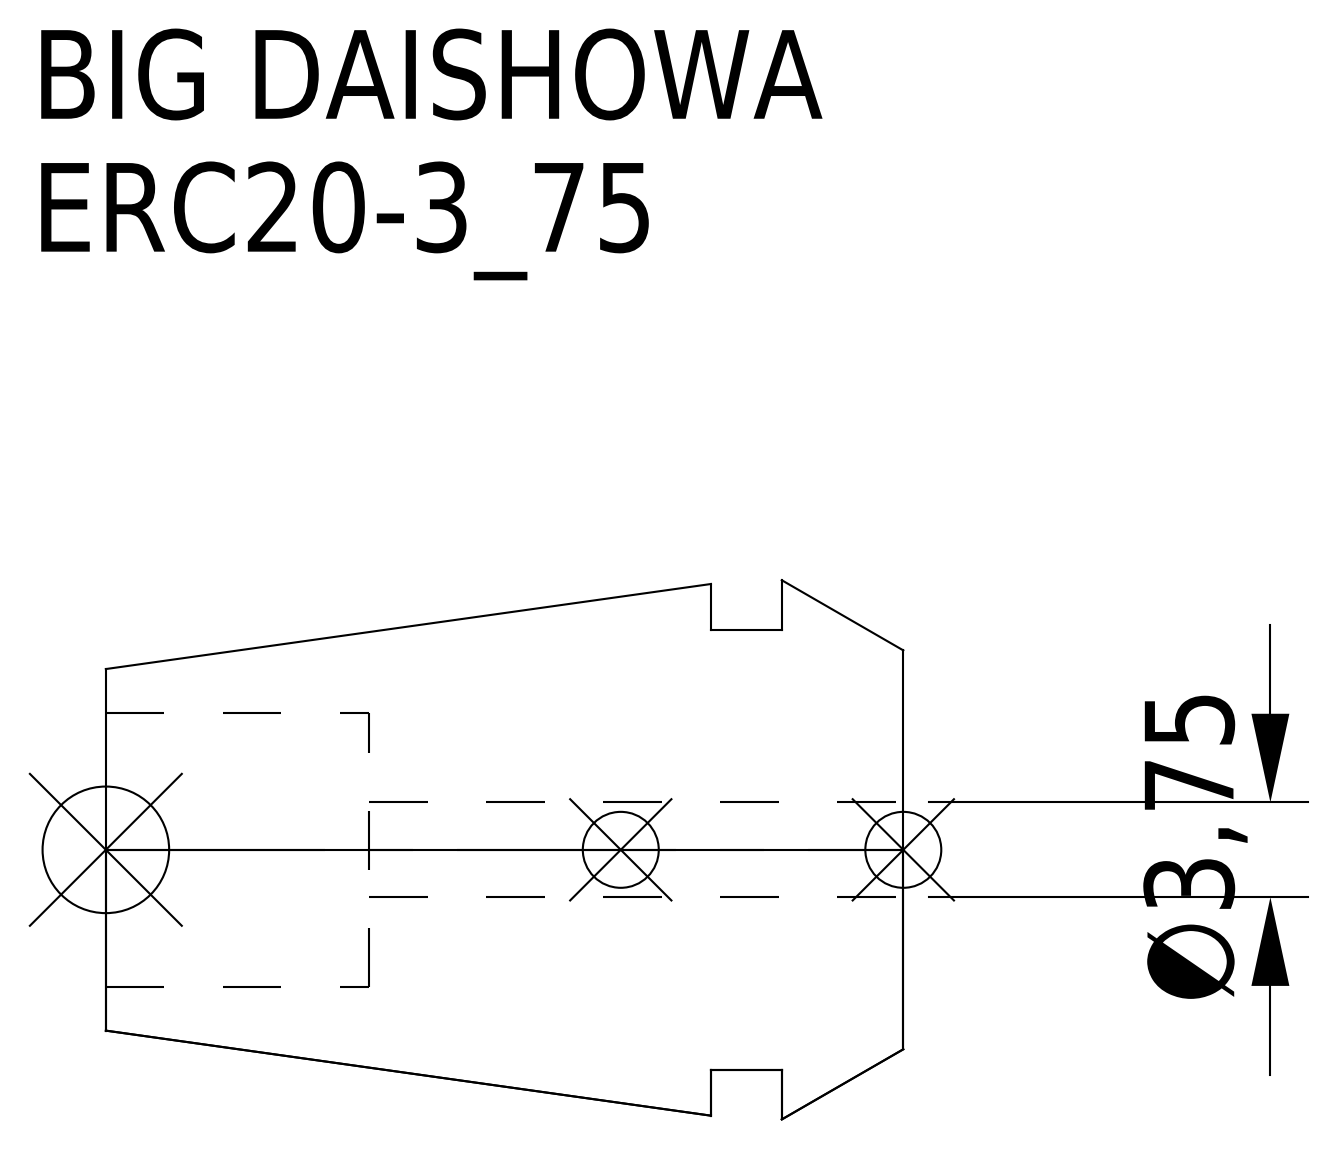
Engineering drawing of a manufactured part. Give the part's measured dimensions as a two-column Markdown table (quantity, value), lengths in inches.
| quantity | value |
| --- | --- |
| part name | ERC20-3_75 |
| STEP written by | CREO PARAMETRIC BY PTC INC, 2016380 (AUTOMOTIVE_DESIGN) |
| units | inches |
| bodies | 1 solid, 15 faces (5 planar, 6 cylindrical, 4 other) |
| overall size | 1.24 × 0.839 × 0.839 |
| volume | 0.409 in³ |
| surface area | 4.611 in² |
| round holes (diameter × count) | 0.148 × 1, 0.425 × 1 |
| round bosses / shafts (diameter × count) | 0.685 × 1 |
| main face-to-face distances | 0.189, 0.299, 0.11, 0.83, 0.641, 0.531, 1.24, 1.051, 0.941, 0.41 |
